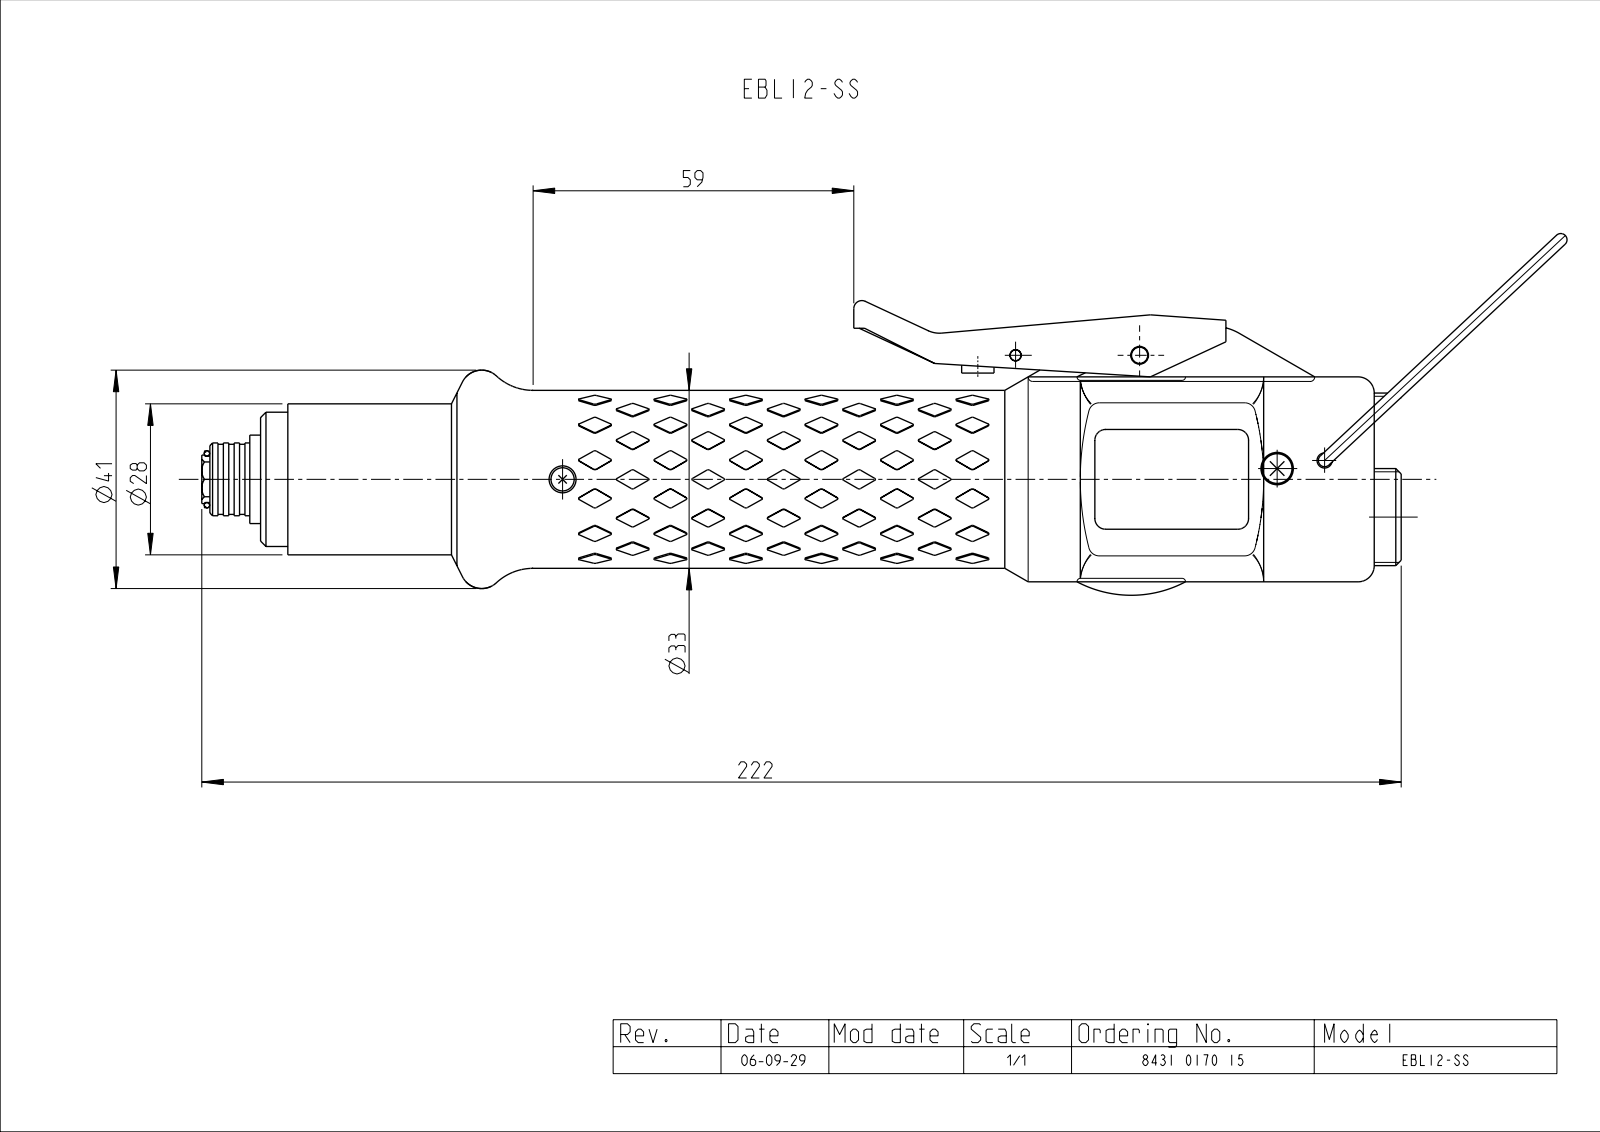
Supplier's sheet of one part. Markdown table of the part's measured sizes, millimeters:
| quantity | value |
| --- | --- |
| part name | 84310170011_M_S |
| STEP written by | PRO/ENGINEER BY PARAMETRIC TECHNOLOGY CORPORATION, 2006300 (CONFIG_CONTROL_DESIGN) |
| units | millimeters |
| bodies | 1 solid, 239 faces (51 planar, 69 cylindrical, 119 other) |
| overall size | 269 × 56.91 × 45 |
| volume | 214 504 mm³ |
| surface area | 31 189 mm² |
| round holes (diameter × count) | 14.5 × 1 |
| round bosses / shafts (diameter × count) | 2 × 5, 17 × 2, 38.5 × 1, 33 × 1, 28 × 1, 25 × 1, 13.5 × 1 |
| partial cylindrical surfaces (radius × count) | 1 × 10, 0.4 × 6, 2 × 4, 8 × 4, 20.43 × 3, 3 × 2, 7.74 × 2, 10 × 1 |
| main face-to-face distances | 40.5, 10.25, 30.25, 11.5, 12.5, 20, 29, 34, 1.25, 18.75 |
